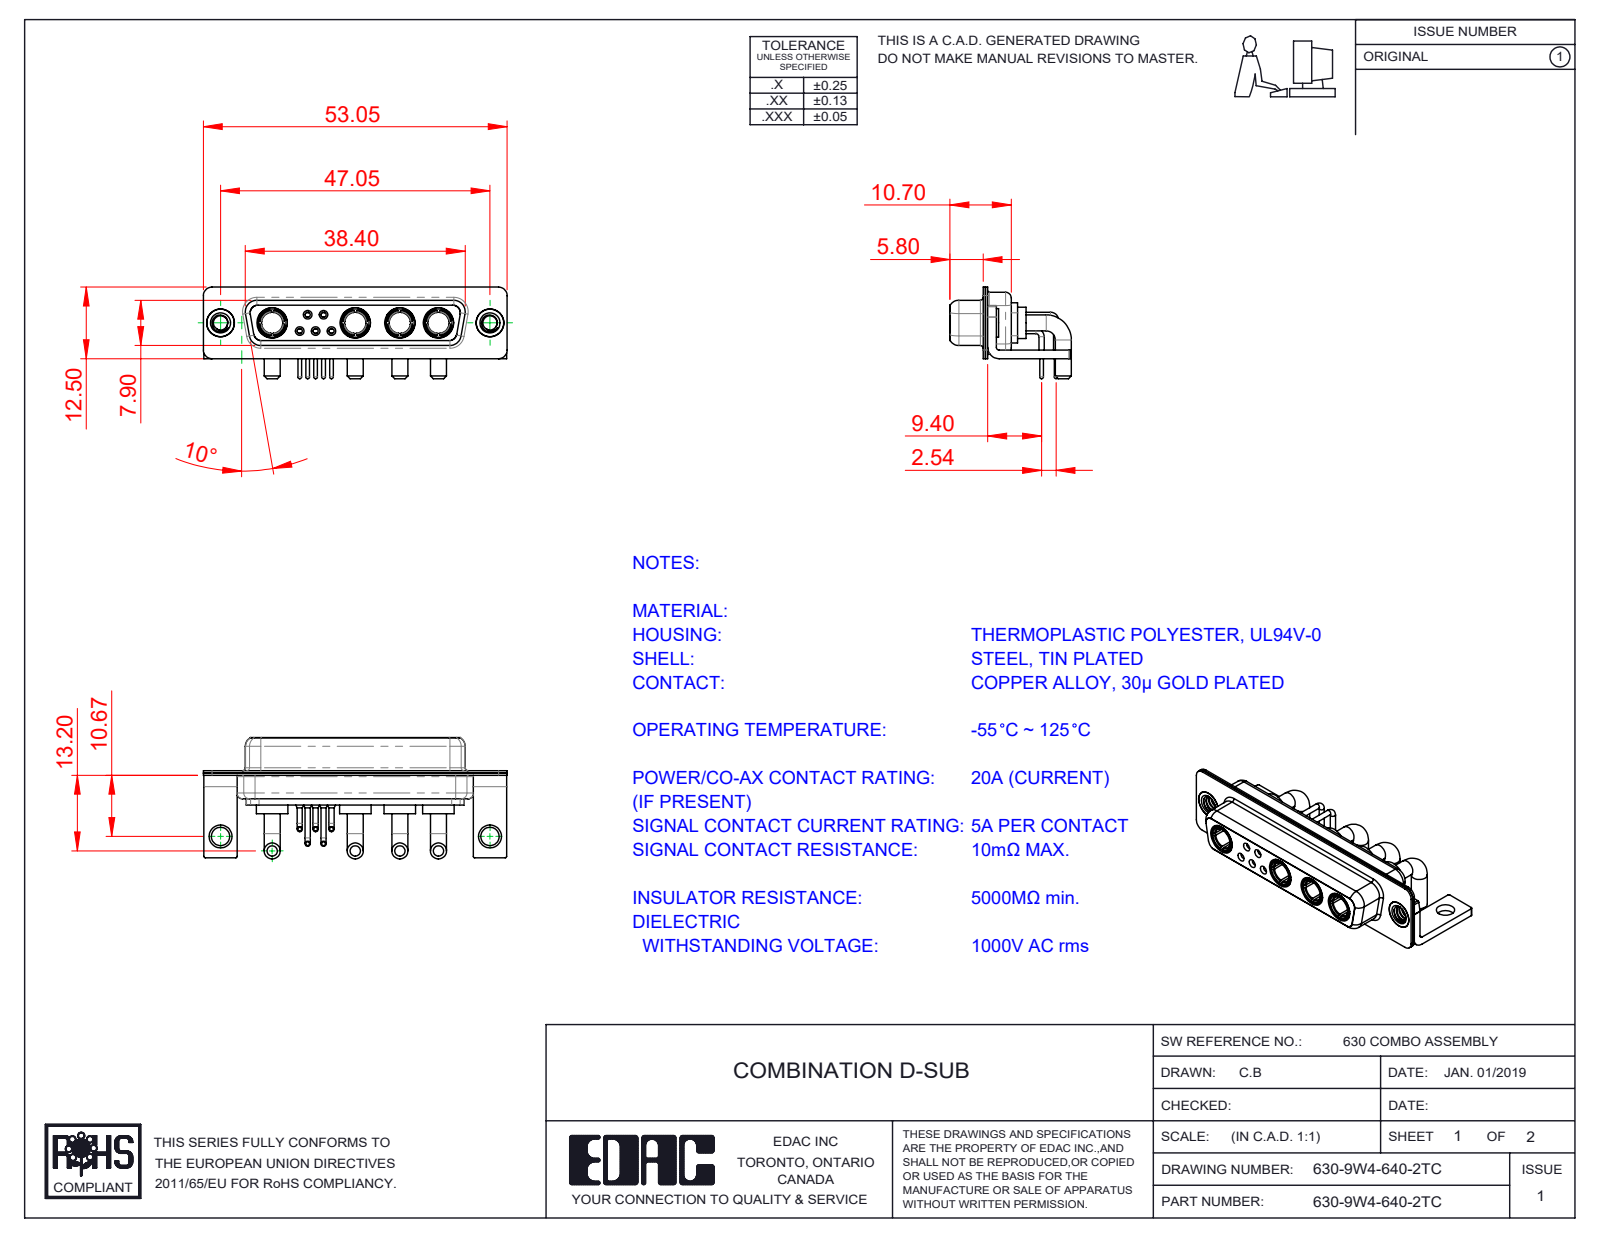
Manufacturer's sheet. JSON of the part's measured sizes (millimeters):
{"part_name": "Power Socket_20A RA; 630-9W4-640-2TC; 630Combo Contact Row 2; 630Combo Contact Row 1 (+5 more)", "step_written_by": "SolidWorks 2020 (CONFIG_CONTROL_DESIGN)", "units": "millimeters", "bodies": {"solids": 20, "faces": 894, "planar": 278, "cylindrical": 370, "other": 246}, "overall_size": [53.05, 21.2, 16], "volume_mm3": 4285, "surface_area_mm2": 9433, "round_holes": [[4.85, 6], [0.9, 5], [1.1, 5], [1.5, 5], [2, 5], [3.7, 4], [5.3, 4], [1.6, 3], [1.7, 2], [2.5, 2], [3.2, 2], [4, 2]], "round_bosses_or_shafts": [[2.8, 8], [0.9, 5], [0.65, 5], [5.5, 4], [5.2, 4], [4.96, 4], [4.75, 4], [3.75, 4]], "partial_cylinders_radius": [[0.25, 16], [1.5, 16], [2, 13], [1.35, 8], [1.6, 8], [0.5, 5], [0.6, 4], [0.65, 4]], "face_to_face_distances": [0.4, 0.45, 1.4, 8.45, 1.8, 0.8, 8.9, 1.5, 7.05, 6.2], "hole_center_spacings": [3.16, 2.77, 47.05, 4.4, 5.02, 5.03, 5.04, 5.54]}
